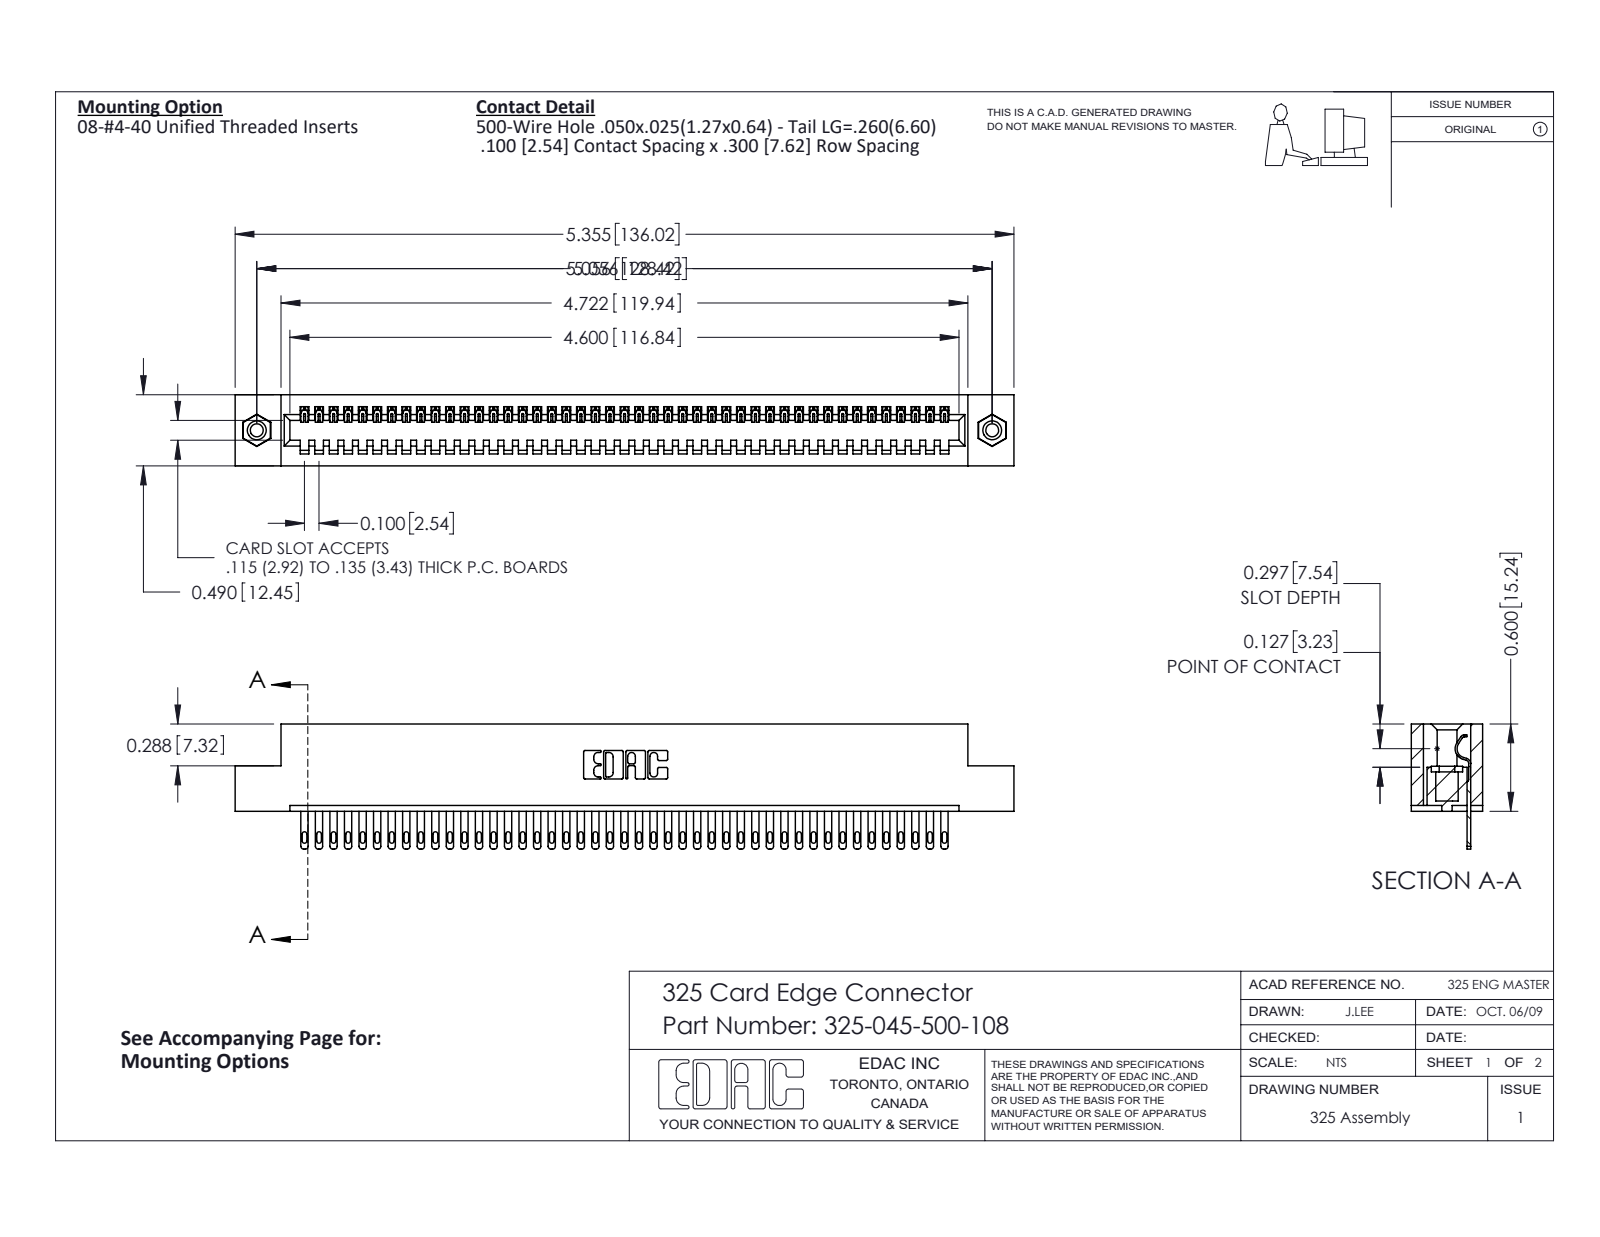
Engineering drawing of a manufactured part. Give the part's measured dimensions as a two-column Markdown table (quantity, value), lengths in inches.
| quantity | value |
| --- | --- |
| part name | 325-292-001_325-293-100; 325-045-500-108; 345-250-001_345-250-003-102; 325 Part_TI |
| STEP written by | SolidWorks 2016 (CONFIG_CONTROL_DESIGN) |
| units | inches |
| bodies | 48 solids, 2604 faces (1722 planar, 866 cylindrical, 16 other) |
| overall size | 5.355 × 0.86 × 0.49 |
| volume | 1.056 in³ |
| surface area | 29.58 in² |
| round holes (diameter × count) | 0.089 × 2, 0.125 × 2, 0.16 × 2 |
| round bosses / shafts (diameter × count) | 0.155 × 2 |
| partial cylindrical surfaces (radius × count) | 0.006 × 90, 0.016 × 90, 0.02 × 90, 0.01 × 22, 0.007 × 6, 0.031 × 6, 0.026 × 3, 0.014 × 1 |
| main face-to-face distances | 0.083, 0.407, 0.49, 0.3, 0.107, 0.383, 0.025, 0.325, 0.56, 0.263 |
| hole center spacings | 5.056 |
